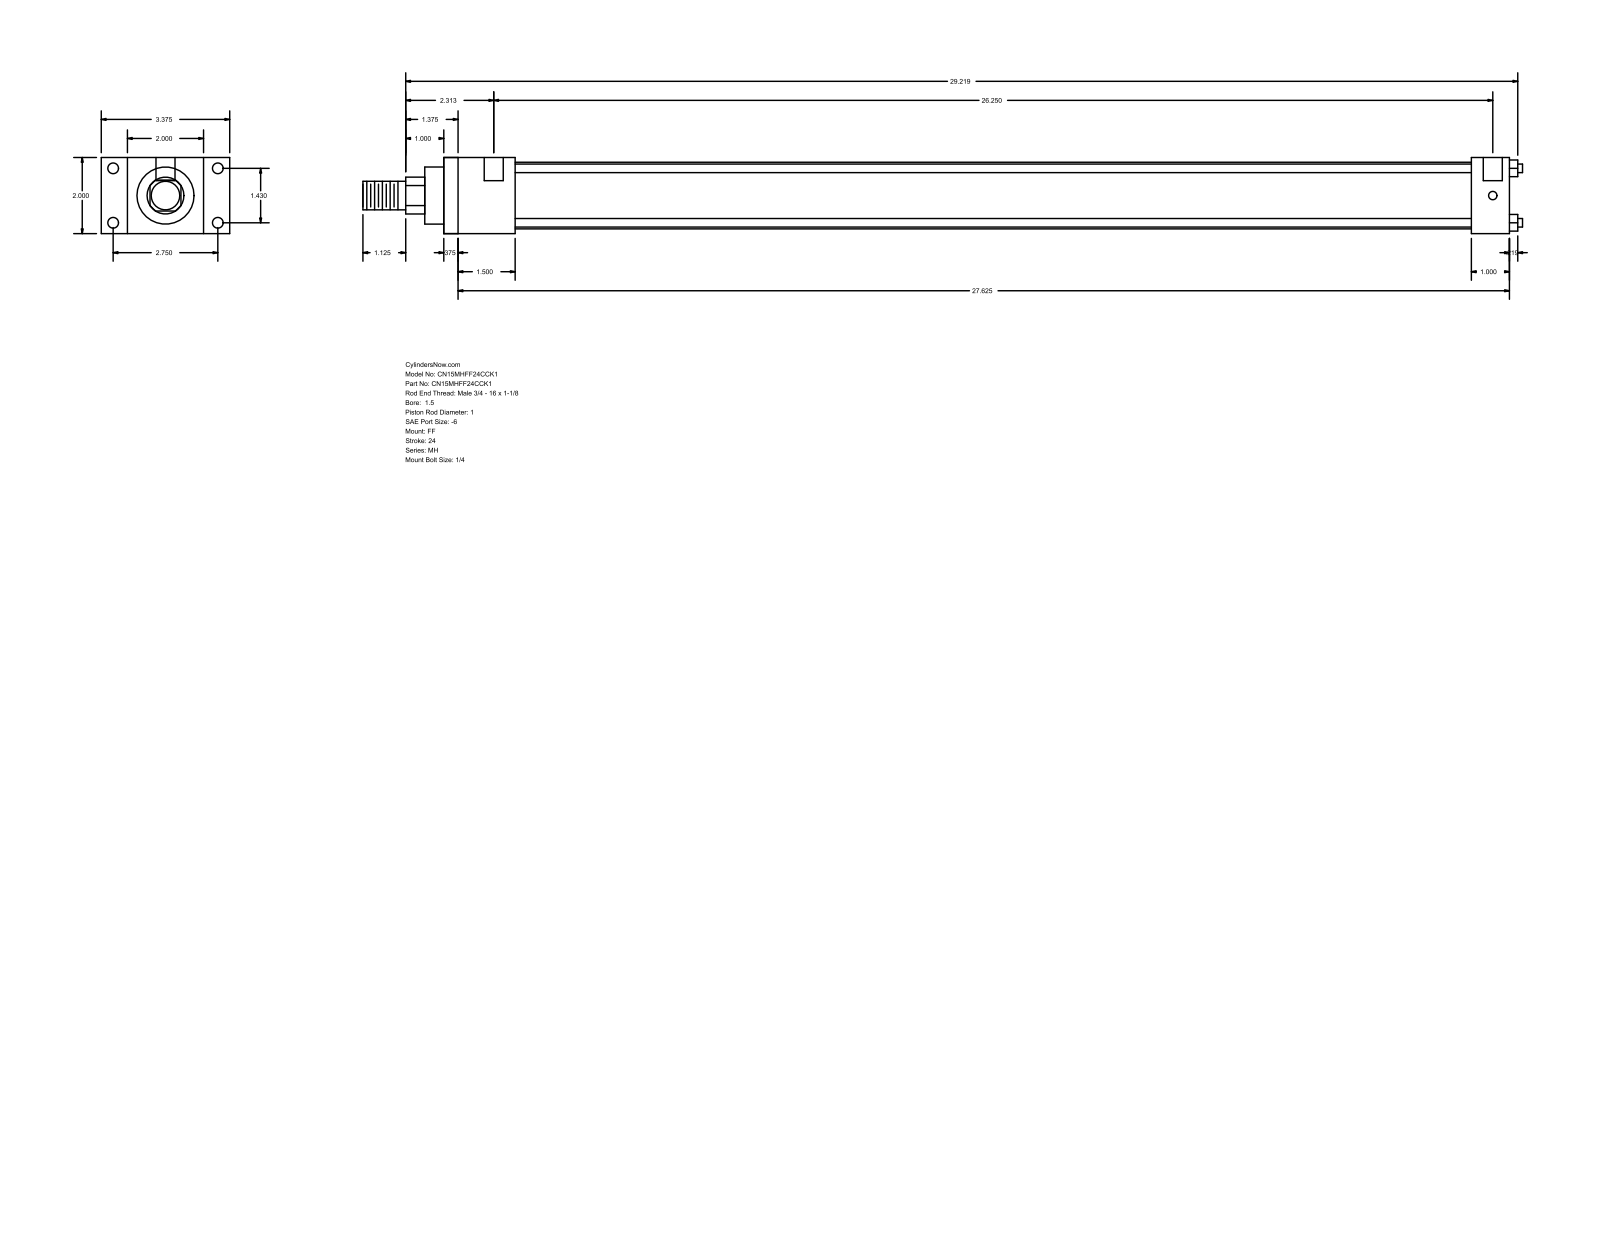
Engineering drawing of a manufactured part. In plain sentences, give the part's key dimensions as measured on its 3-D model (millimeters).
The part is named "MH_FF__0150_1". Its 3-D file was written by "GSSL Pune (CONFIG_CONTROL_DESIGN)". It is 0 solids with 92 faces: 64 planar, 28 cylindrical and 0 other. Overall it measures 773.91 by 85.72 by 50.8 millimeters. Round holes: 4 of diameter 5.56, 4 of diameter 7.14, 2 of diameter 12.7. Round bosses or shafts: 4 of diameter 5.71, 1 of diameter 44.45, 1 of diameter 38.1, 1 of diameter 25.4, 1 of diameter 19.05. Partial cylindrical surfaces (rounded edges, fillets, slot ends): 1 of radius 12.29. The main face-to-face distances are 50.8, 711.2, 9.52, 701.68, 25.4, 17.46, 68.26, 47.63, 38.11, 663.57. The hole center spacings are 36.32, 69.84, 78.72, 669.93, 3.18, 666.75.
